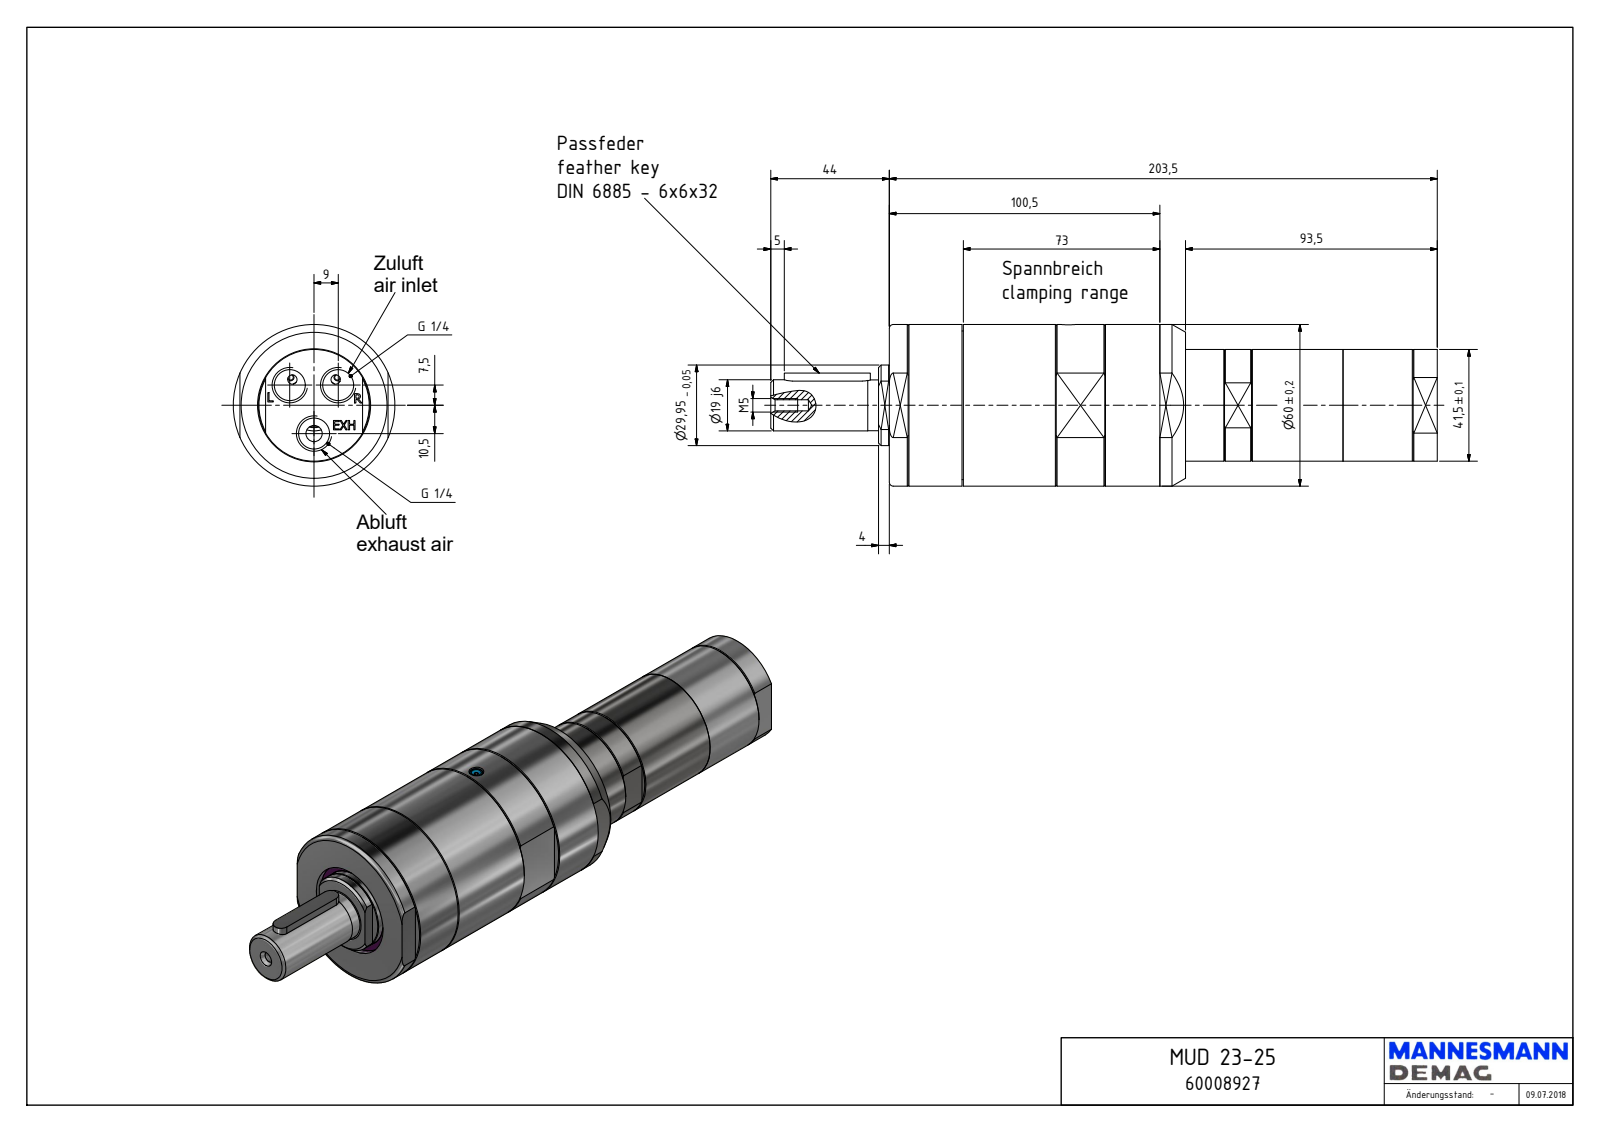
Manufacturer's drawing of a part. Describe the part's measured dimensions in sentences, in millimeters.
The part is named "MUD 23-25_60008927". Its 3-D file was written by "Autodesk Inventor 2018 (AUTOMOTIVE_DESIGN)". It is 1 solid with 477 faces: 202 planar, 229 cylindrical and 46 other. Overall it measures 247.5 by 60 by 60 millimeters. Its volume is 442 586 cubic millimeters and its surface area 46 422 square millimeters. Round holes: 3 of diameter 11.45, 1 of diameter 1.55, 1 of diameter 4.13, 1 of diameter 5.5, 1 of diameter 35, 1 of diameter 42. Round bosses or shafts: 1 of diameter 60, 1 of diameter 55.18, 1 of diameter 41.5, 1 of diameter 29.95, 1 of diameter 19, 1 of diameter 18.8, 1 of diameter 5, 1 of diameter 4. Partial cylindrical surfaces (rounded edges, fillets, slot ends): 94 of radius 11.68, 2 of radius 3, 1 of radius 24.93, 1 of radius 24.96. The main face-to-face distances are 110, 93.5, 203.5, 55, 9.5, 27.5, 82.5, 176, 31, 45.5. The hole center spacings are 11.72, 20.12, 10.5, 18.
